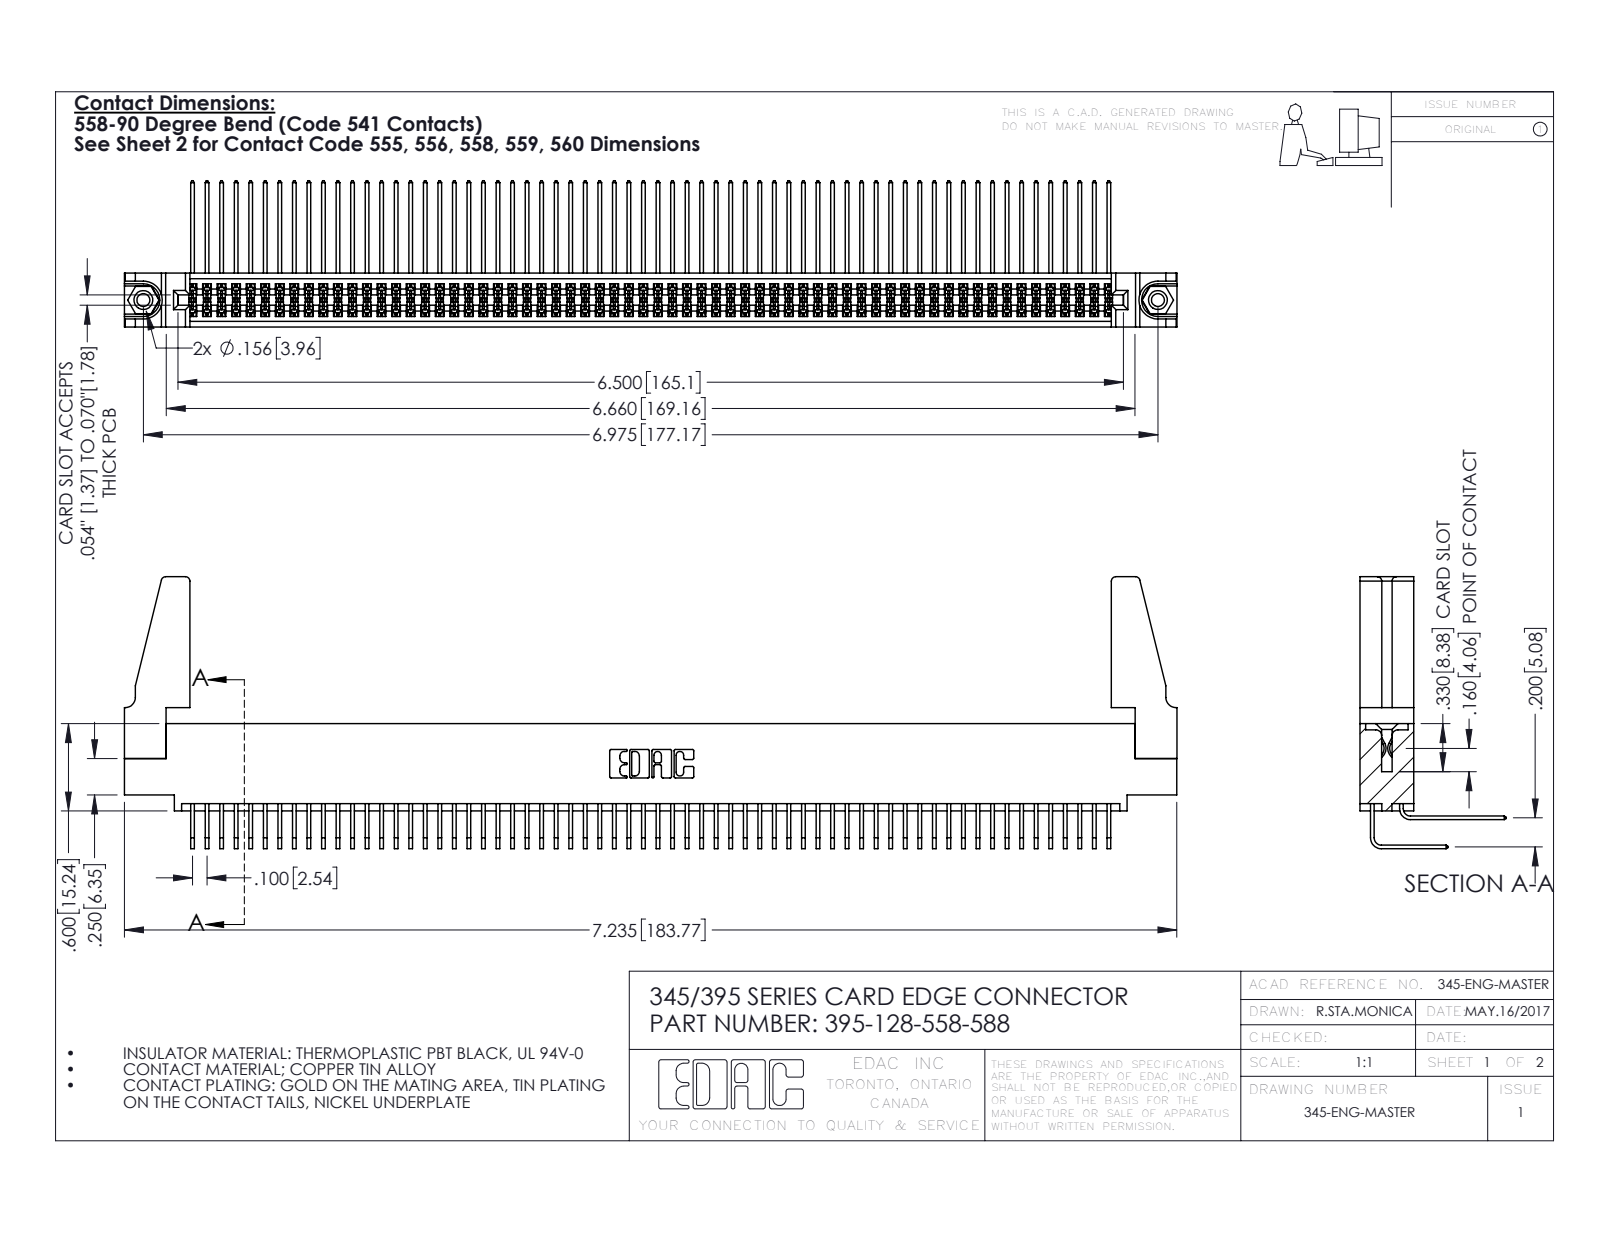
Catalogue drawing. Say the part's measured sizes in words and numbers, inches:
The part is named "345 Part_0.110 Offset - 0.156 Dia-TH; 345-292-001_558 Tail - 2; 345-250-001_345-250-001-102; 395-128-558-588 (+2 more)". Its 3-D file was written by "SolidWorks 2016 (CONFIG_CONTROL_DESIGN)". It is 133 solids with 6910 faces: 4636 planar, 2258 cylindrical and 16 other. Overall it measures 7.236 by 1.869 by 1.005 inches. Its volume is 1.341 cubic inches and its surface area 53.92 square inches. Round holes: 2 of diameter 0.089, 2 of diameter 0.125, 2 of diameter 0.156, 1 of diameter 0.064. Round bosses or shafts: 2 of diameter 0.155. Partial cylindrical surfaces (rounded edges, fillets, slot ends): 193 of radius 0.006, 22 of radius 0.01, 8 of radius 0.03, 6 of radius 0.007, 6 of radius 0.031, 3 of radius 0.026, 2 of radius 0.014, 2 of radius 0.019. The main face-to-face distances are 0.072, 0.298, 0.2, 0.37, 0.098, 0.272, 0.025, 0.225, 0.025, 0.175. The hole center spacings are 0.27, 6.739, 6.975.
